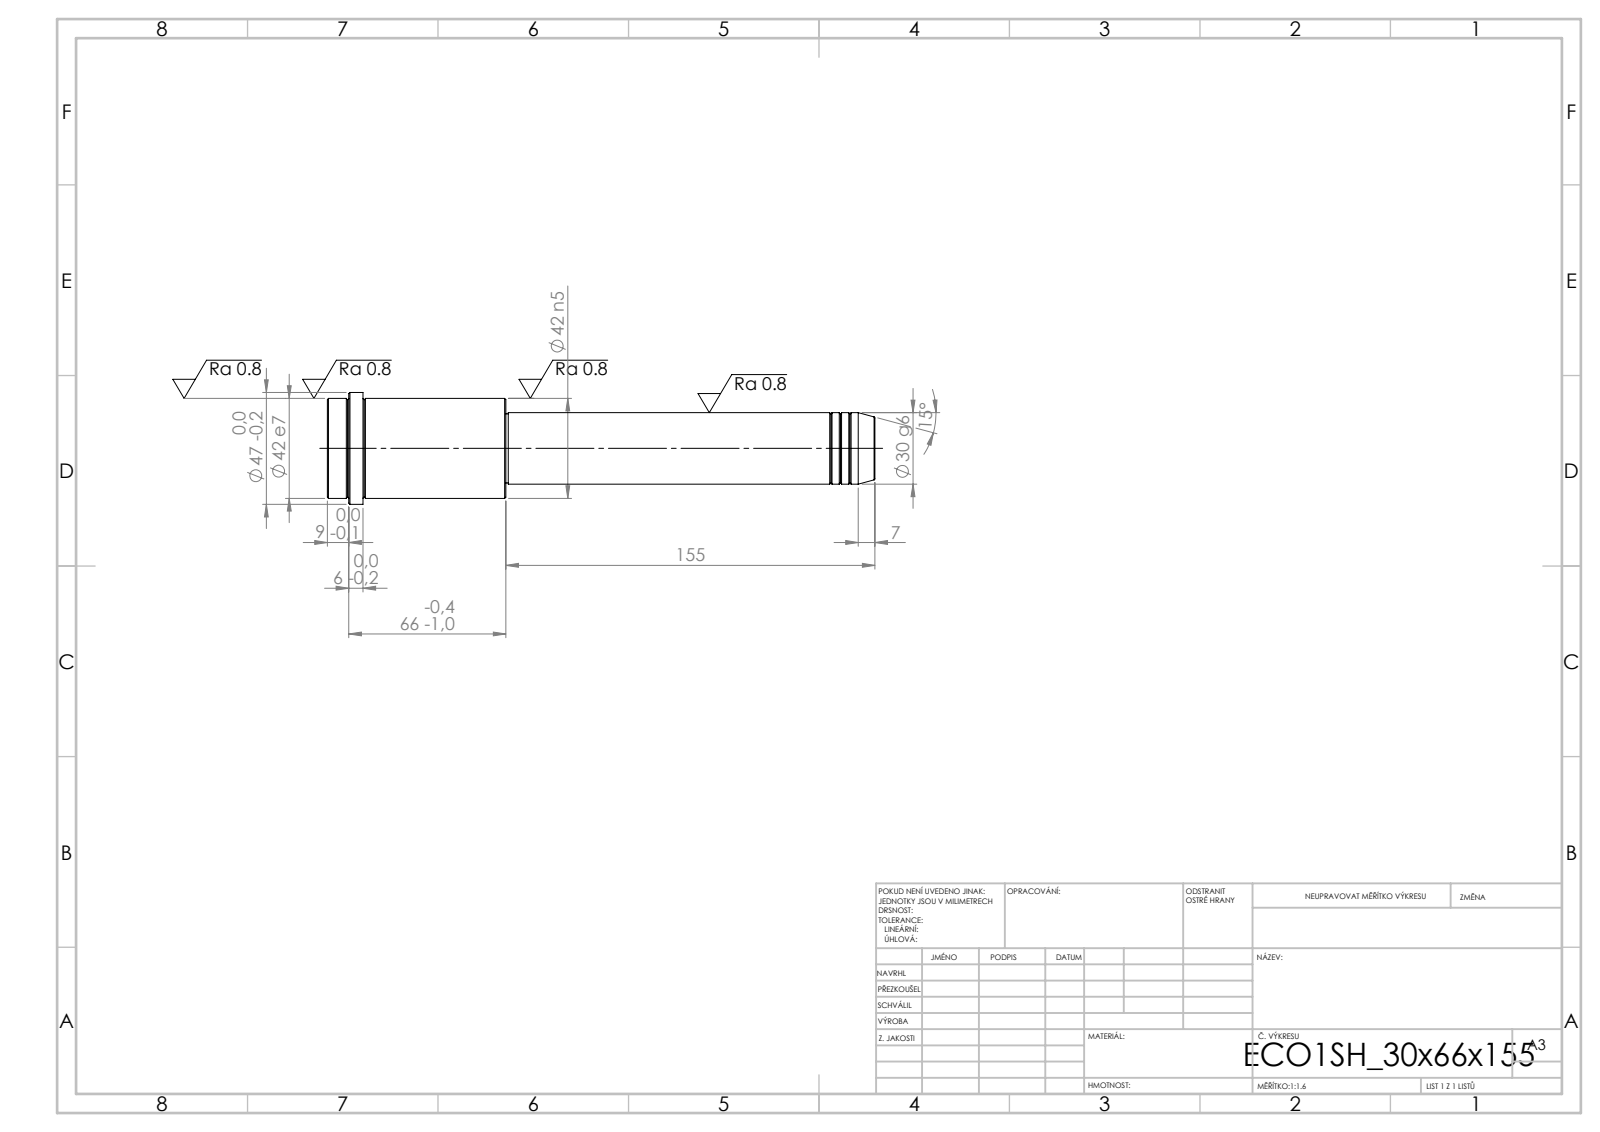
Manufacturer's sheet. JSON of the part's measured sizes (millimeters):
{"step_written_by": "SolidWorks 2019 (CONFIG_CONTROL_DESIGN)", "units": "millimeters", "bodies": {"solids": 1, "faces": 52, "planar": 6, "cylindrical": 16, "other": 30}, "overall_size": [230, 47, 47], "volume_mm3": 214664, "surface_area_mm2": 28138, "round_bosses_or_shafts": [[47, 1], [42, 1], [30, 1], [29, 1]], "face_to_face_distances": [75, 155, 230, 215, 60, 15, 221, 66, 6, 9]}
